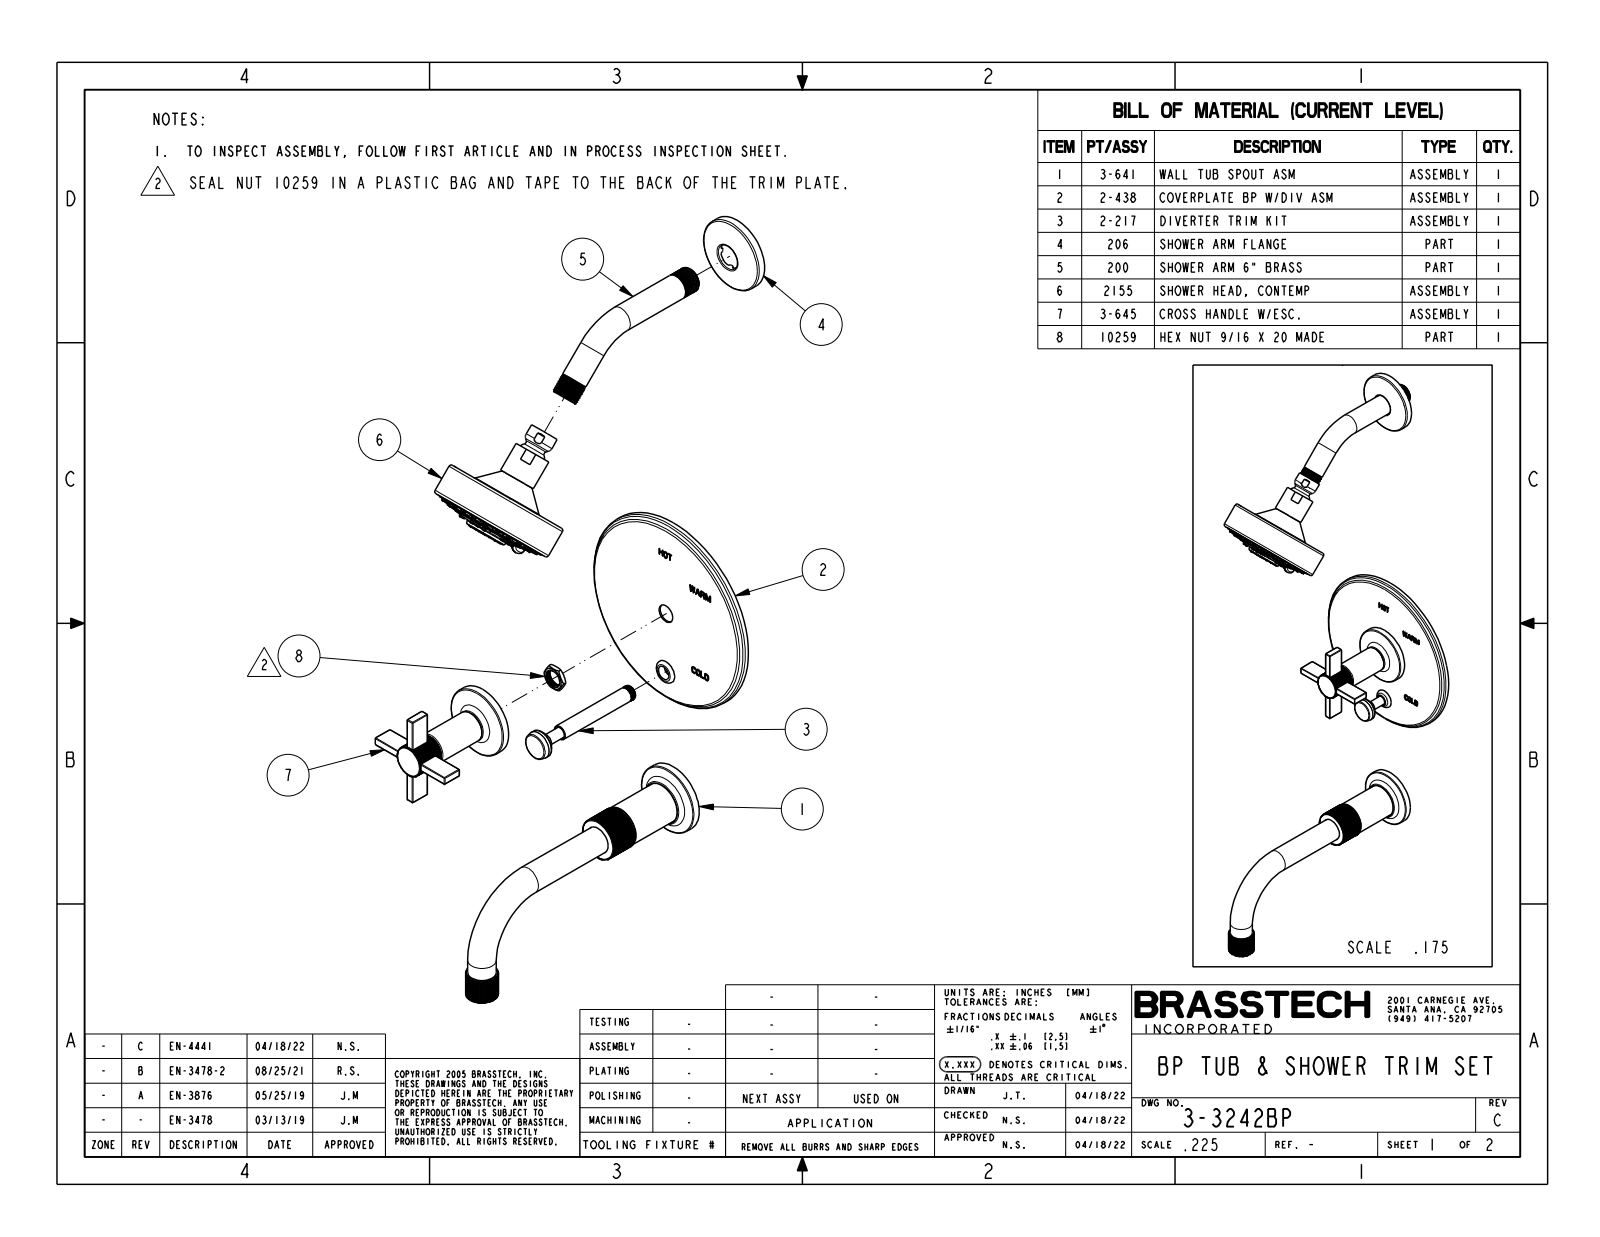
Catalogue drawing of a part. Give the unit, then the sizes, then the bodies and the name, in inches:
Units: inches
Overall size (bounding box): 23.45 × 11.287 × 6.5
Round holes (diameter × count): ⌀0.043 ×32, ⌀0.098 ×15, ⌀0.059 ×12, ⌀0.079 ×8, ⌀0.096 ×8, ⌀0.187 ×8, ⌀0.118 ×7, ⌀0.11 ×5, ⌀0.15 ×5, ⌀0.15 ×3, ⌀0.252 ×3, ⌀0.276 ×3
Round bosses / shafts (diameter × count): ⌀0.142 ×39, ⌀0.165 ×23, ⌀0.138 ×5, ⌀0.315 ×3, ⌀0.244 ×3, ⌀2.25 ×2, ⌀1.812 ×2, ⌀1 ×2
Partial cylindrical surfaces — rounded edges, fillets, slot ends (radius × count): R0.02 ×52, R0.02 ×40, R0.012 ×29, R0.03 ×16, R0.083 ×15, R0.007 ×14, R0.1 ×12, R0.079 ×9
Main face-to-face distances: 0.05, 0.098, 0.208, 0.698, 0.04, 0.658, 0.45, 0.49, 0.307, 0.757
Hole centre spacings: 0.378, 0.421, 0.274, 0.21, 0.274, 0.37, 0.422, 0.607
Volume: 21.02 in³ · Surface area: 779.8 in²
Bodies: 76 solids, 10633 faces (4694 planar, 3026 cylindrical, 2913 other)
Part name (STEP PRODUCT): 13145; 13150; 11670; 20-422_ASM (+8 more)
STEP written by: CREO PARAMETRIC BY PTC INC, 2018400 (CONFIG_CONTROL_DESIGN)
